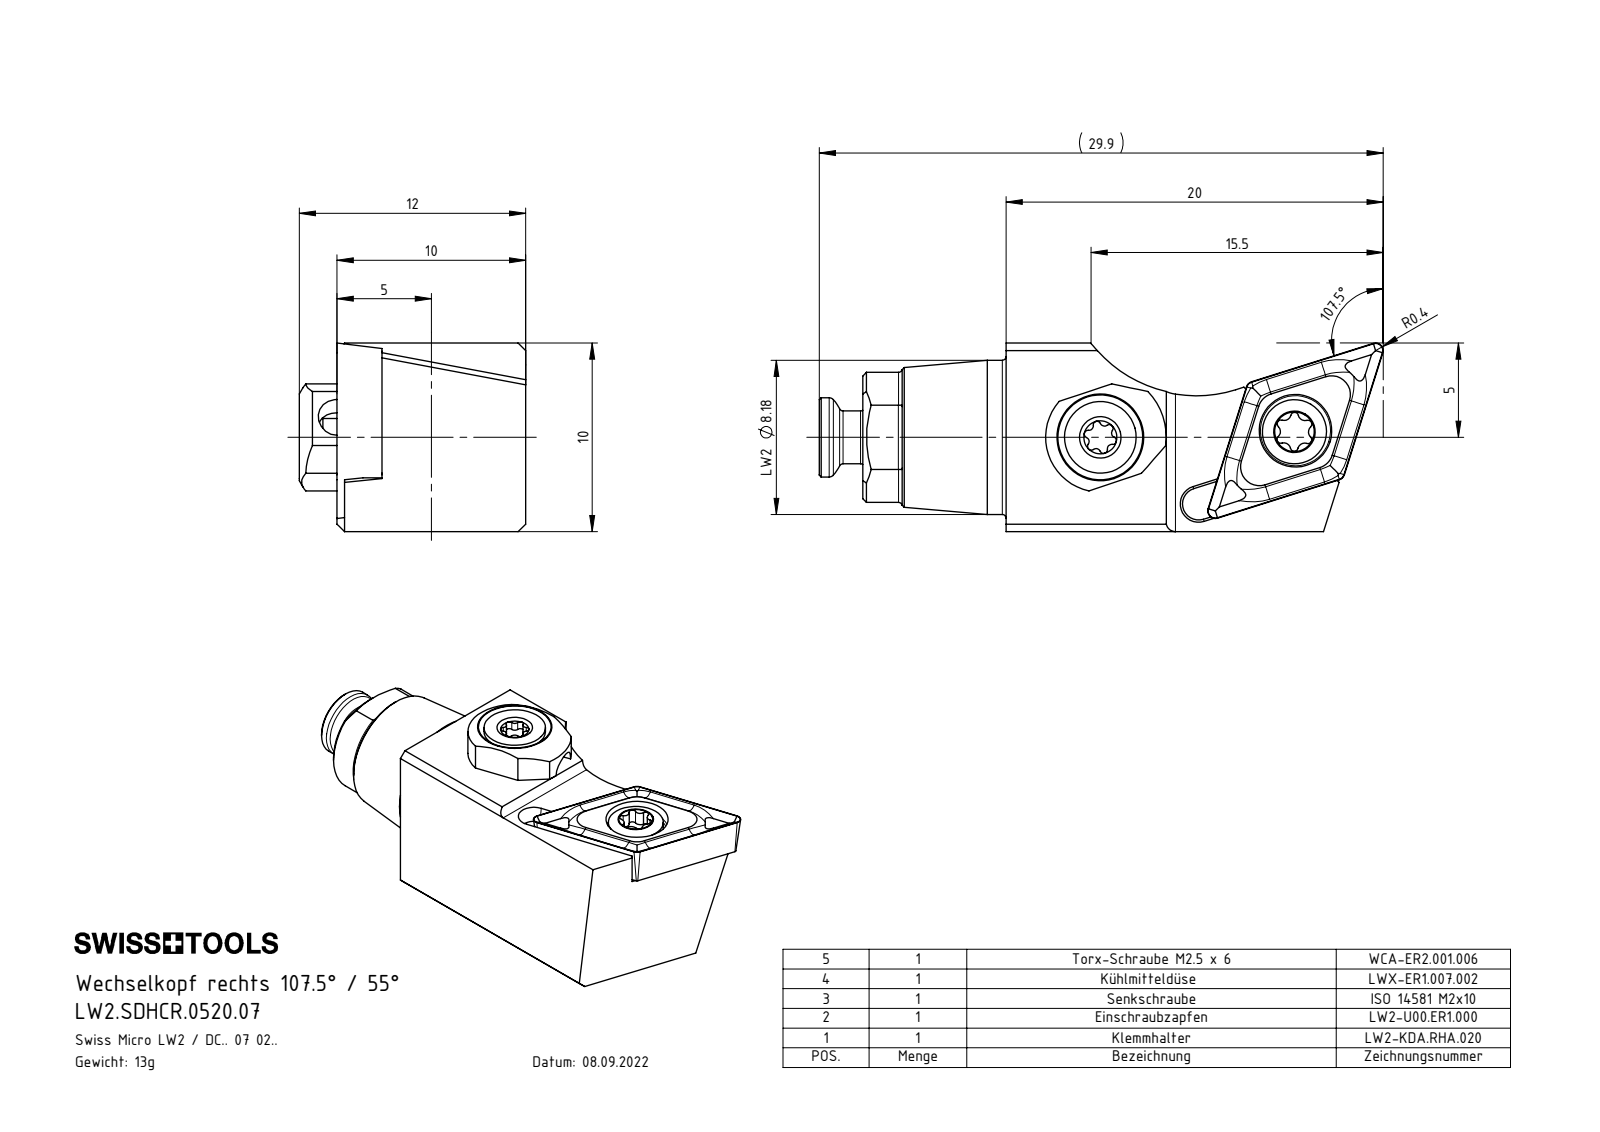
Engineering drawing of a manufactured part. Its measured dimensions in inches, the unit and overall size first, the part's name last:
Units: inches
Overall size (bounding box): 1.177 × 0.472 × 0.394
Round holes (diameter × count): ⌀0.039 ×1, ⌀0.059 ×1, ⌀0.063 ×1, ⌀0.081 ×1, ⌀0.11 ×1, ⌀0.118 ×1, ⌀0.138 ×1, ⌀0.152 ×1
Round bosses / shafts (diameter × count): ⌀0.322 ×1, ⌀0.165 ×1, ⌀0.157 ×1, ⌀0.15 ×1, ⌀0.134 ×1, ⌀0.118 ×1, ⌀0.11 ×1, ⌀0.098 ×1
Partial cylindrical surfaces — rounded edges, fillets, slot ends (radius × count): R0.008 ×8, R0.007 ×6, R0.008 ×6, R0.009 ×6, R0.011 ×6, R0.014 ×5, R0.014 ×1, R0.02 ×1
Main face-to-face distances: 0.394, 0.3, 0.094, 0.378, 0.078, 0.016, 0.299, 0.079, 0.043, 0.315
Hole centre spacings: 0.406, 0.408
Volume: 0.108 in³ · Surface area: 2.714 in²
Bodies: 6 solids, 258 faces (66 planar, 93 cylindrical, 99 other)
Part name (STEP PRODUCT): LW2.SDHCR.0520.07; LW2-KDA.RHA.020_A; ISO 14581 - M2x10; LW2-U00.ER1.000_A (+3 more)
STEP written by: SolidWorks 2022 (CONFIG_CONTROL_DESIGN)
